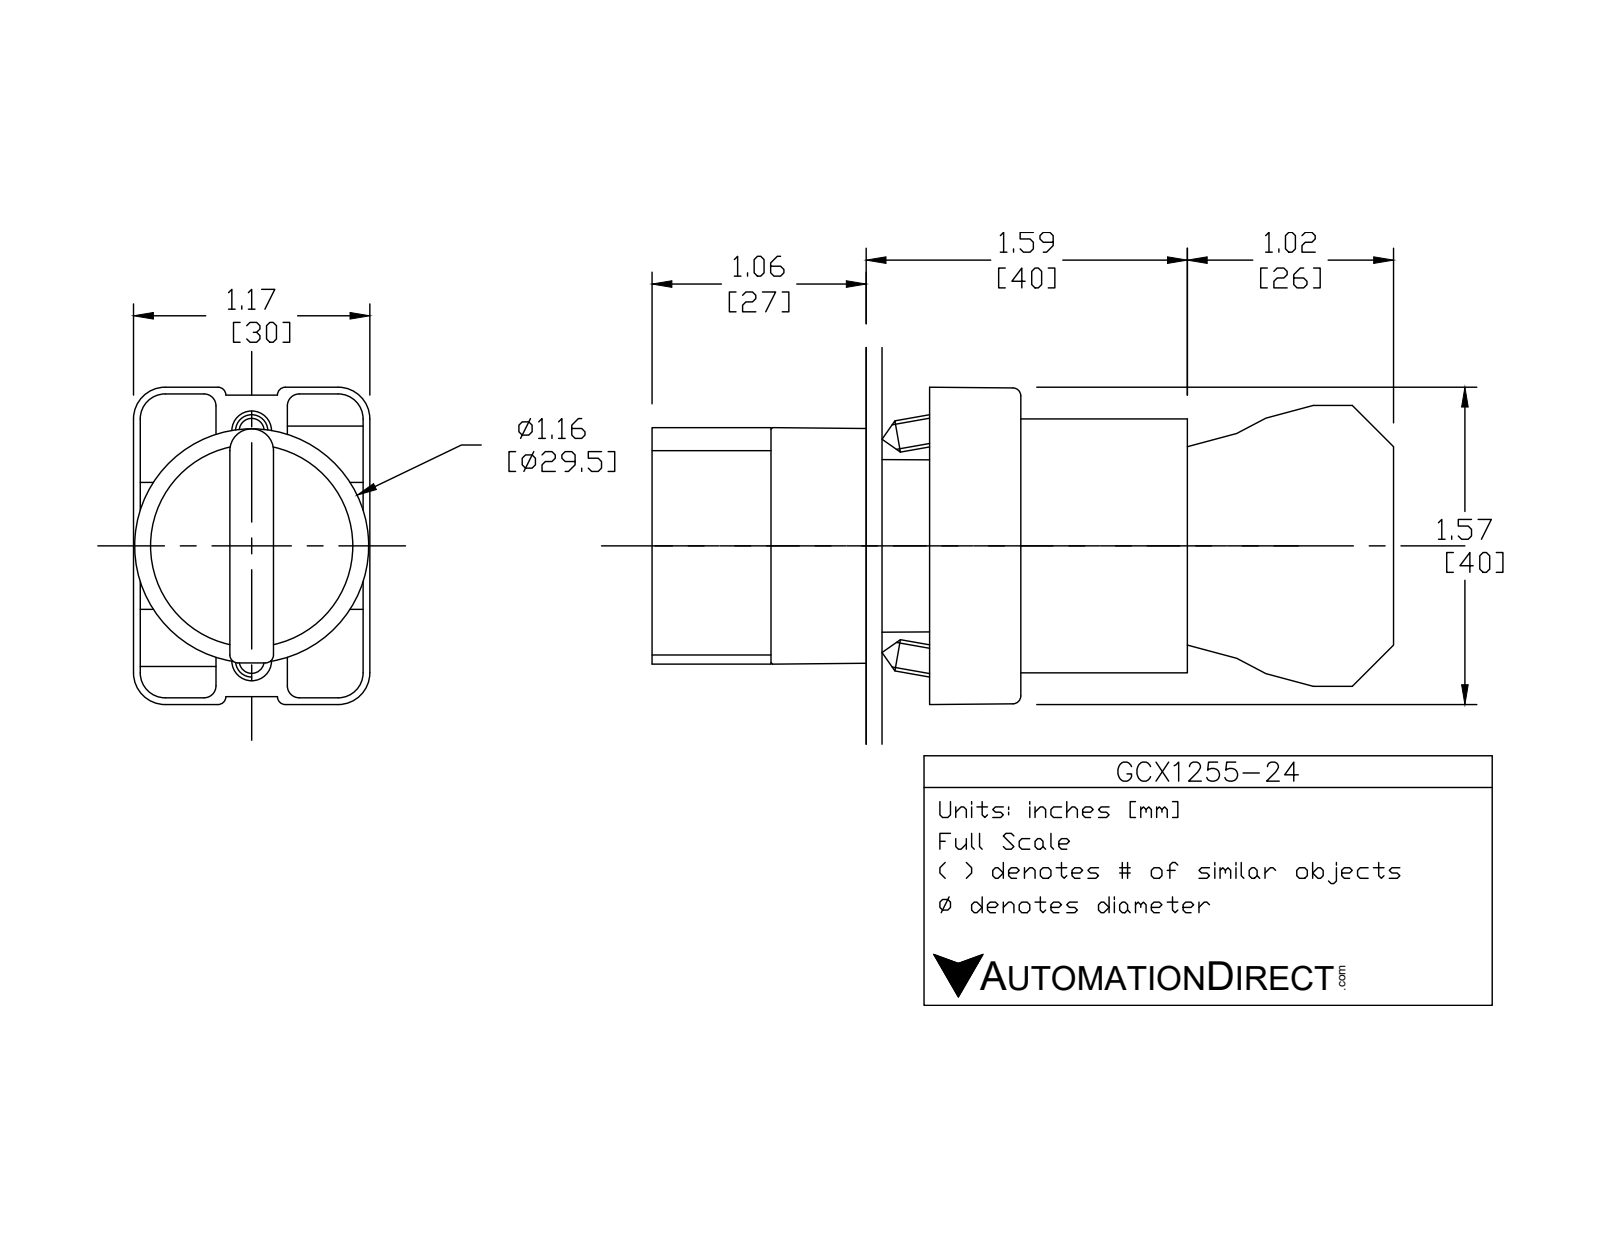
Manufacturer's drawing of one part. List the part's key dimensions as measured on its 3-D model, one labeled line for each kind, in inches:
Part name (STEP PRODUCT): ecx1040; ECX1050; GCX1255 OPERATOR; GCX1255-24 (+1 more)
STEP written by: SolidWorks 2016 (AUTOMOTIVE_DESIGN)
Units: inches
Bodies: 8 solids, 445 faces (263 planar, 151 cylindrical, 31 other)
Overall size (bounding box): 3.653 × 1.581 × 1.177
Volume: 2.799 in³ · Surface area: 39 in²
Round holes (diameter × count): ⌀0.079 ×2, ⌀0.124 ×2, ⌀0.13 ×2, ⌀0.087 ×1, ⌀0.197 ×1, ⌀0.469 ×1, ⌀0.878 ×1, ⌀0.888 ×1, ⌀1.024 ×1
Round bosses / shafts (diameter × count): ⌀0.157 ×4, ⌀1.175 ×1, ⌀1.004 ×1, ⌀0.945 ×1, ⌀0.856 ×1, ⌀0.78 ×1, ⌀0.504 ×1
Partial cylindrical surfaces — rounded edges, fillets, slot ends (radius × count): R0.059 ×24, R0.041 ×12, R0.124 ×12, R0.157 ×12, R0.039 ×9, R0.128 ×2, R0.02 ×1, R0.063 ×1
Main face-to-face distances: 0.827, 2.02, 1.193, 0.579, 1.244, 1.171, 0.472, 0.469, 0.031, 0.033
Hole centre spacings: 0.236, 0.544, 0.472, 0.49
